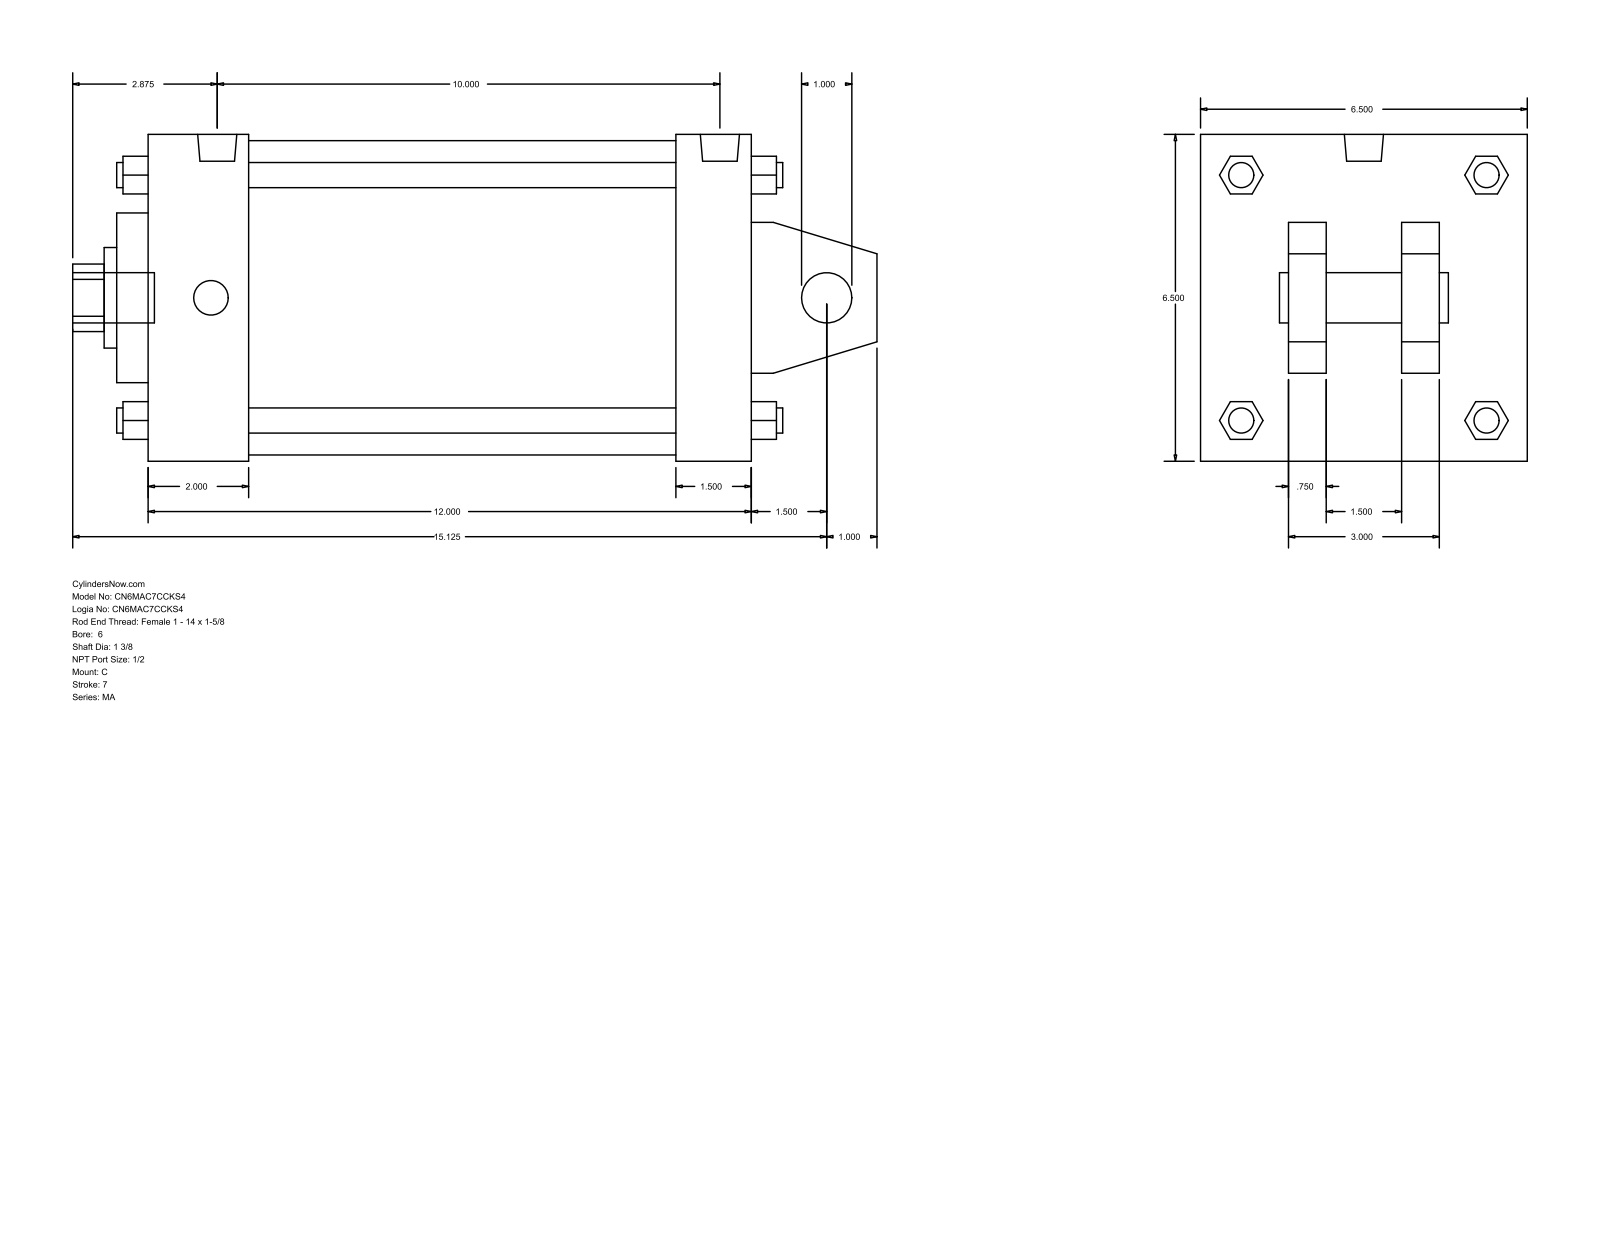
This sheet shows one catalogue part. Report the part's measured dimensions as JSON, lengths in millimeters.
{"part_name": "MA_C__0600_1.375", "step_written_by": "GSSL Pune (CONFIG_CONTROL_DESIGN)", "units": "millimeters", "bodies": {"solids": 0, "faces": 141, "planar": 109, "cylindrical": 32, "other": 0}, "overall_size": [406.4, 165.1, 165.1], "round_holes": [[25.4, 1], [34.92, 1], [50.8, 1], [85.72, 1], [158.75, 1]], "round_bosses_or_shafts": [[17.46, 4], [12.7, 4], [19.77, 2], [25.4, 1]], "partial_cylinders_radius": [[17.06, 1]], "face_to_face_distances": [165.1, 304.8, 38.1, 19.05, 63.5, 101.6, 50.8, 120.65, 44.45, 266.7]}
